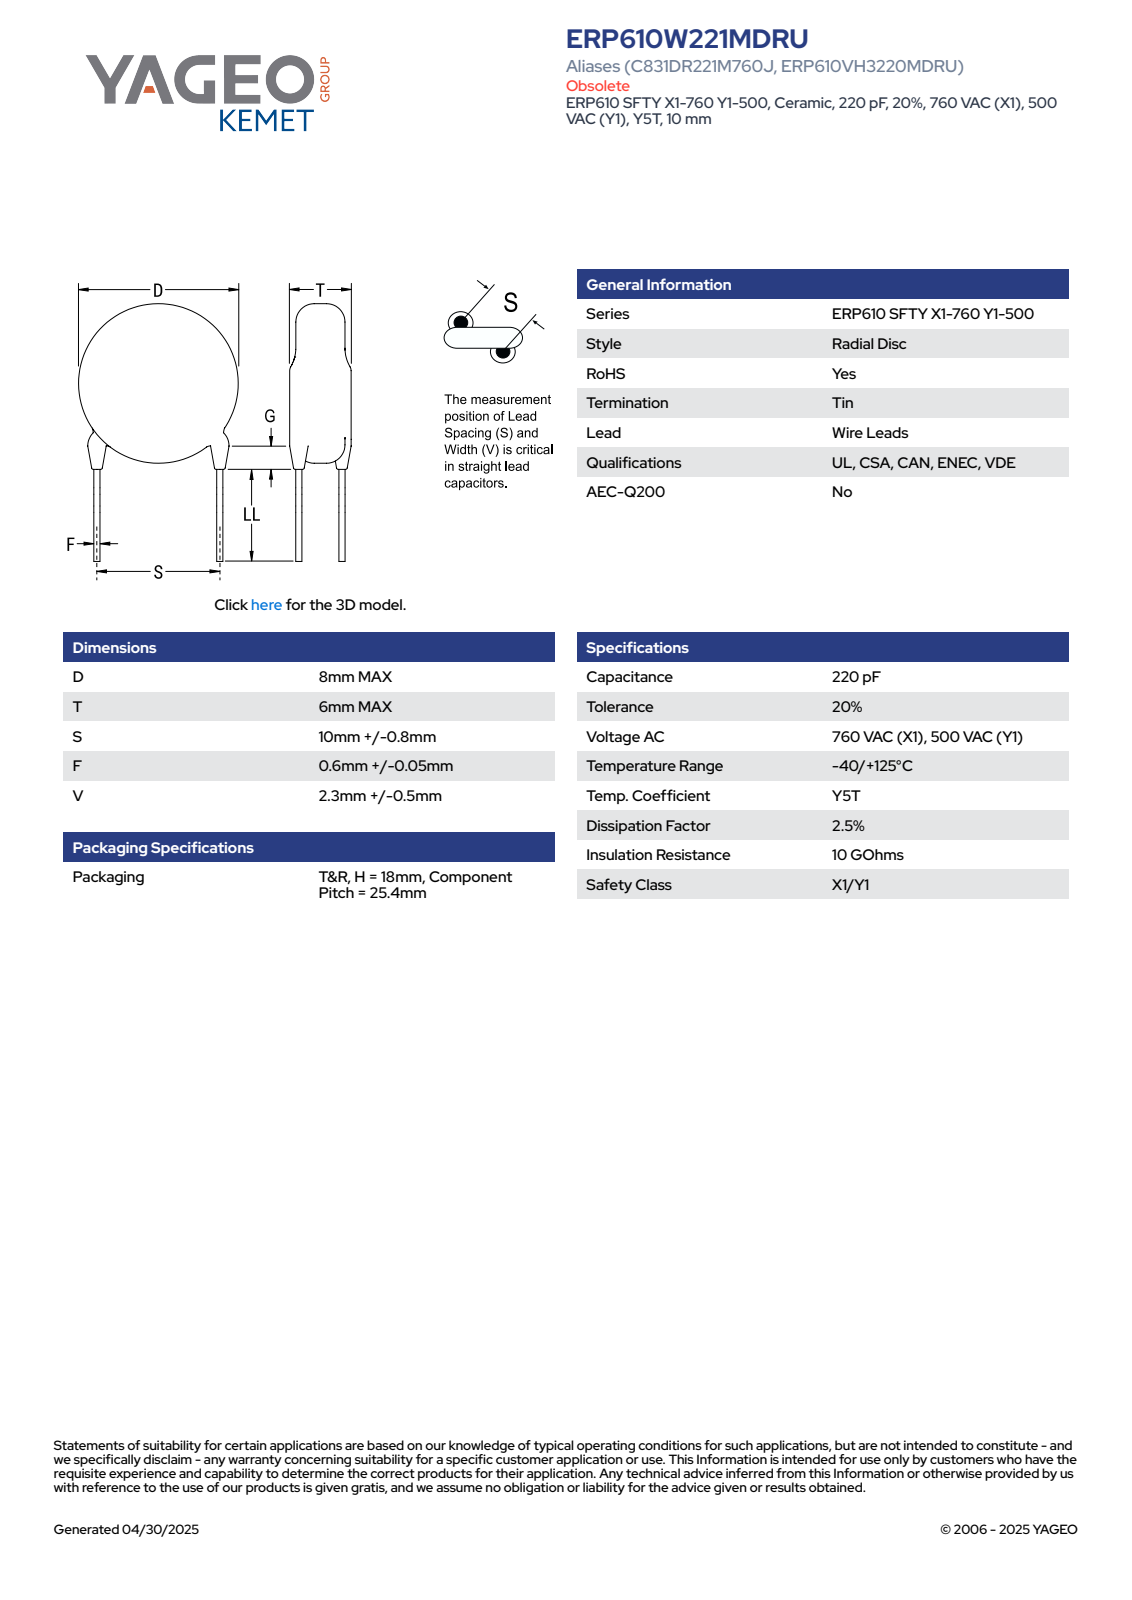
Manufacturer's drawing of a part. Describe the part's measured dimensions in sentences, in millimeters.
The part is named "CCD_KST_8X6_D8T6S10LL11F0.65G3V2.8". Its 3-D file was written by "SolidWorks 2014 (AUTOMOTIVE_DESIGN)". It is 4 solids with 81 faces: 63 planar, 6 cylindrical and 12 other. Overall it measures 19.21 by 10.25 by 6 millimeters. Its volume is 302 cubic millimeters and its surface area 293 square millimeters. Round bosses or shafts: 2 of diameter 0.65, 1 of diameter 8. The main face-to-face distances are 6, 1, 15.71, 14.71, 1.12, 4.07, 0.81, 0.62, 0.36, 2.95.
